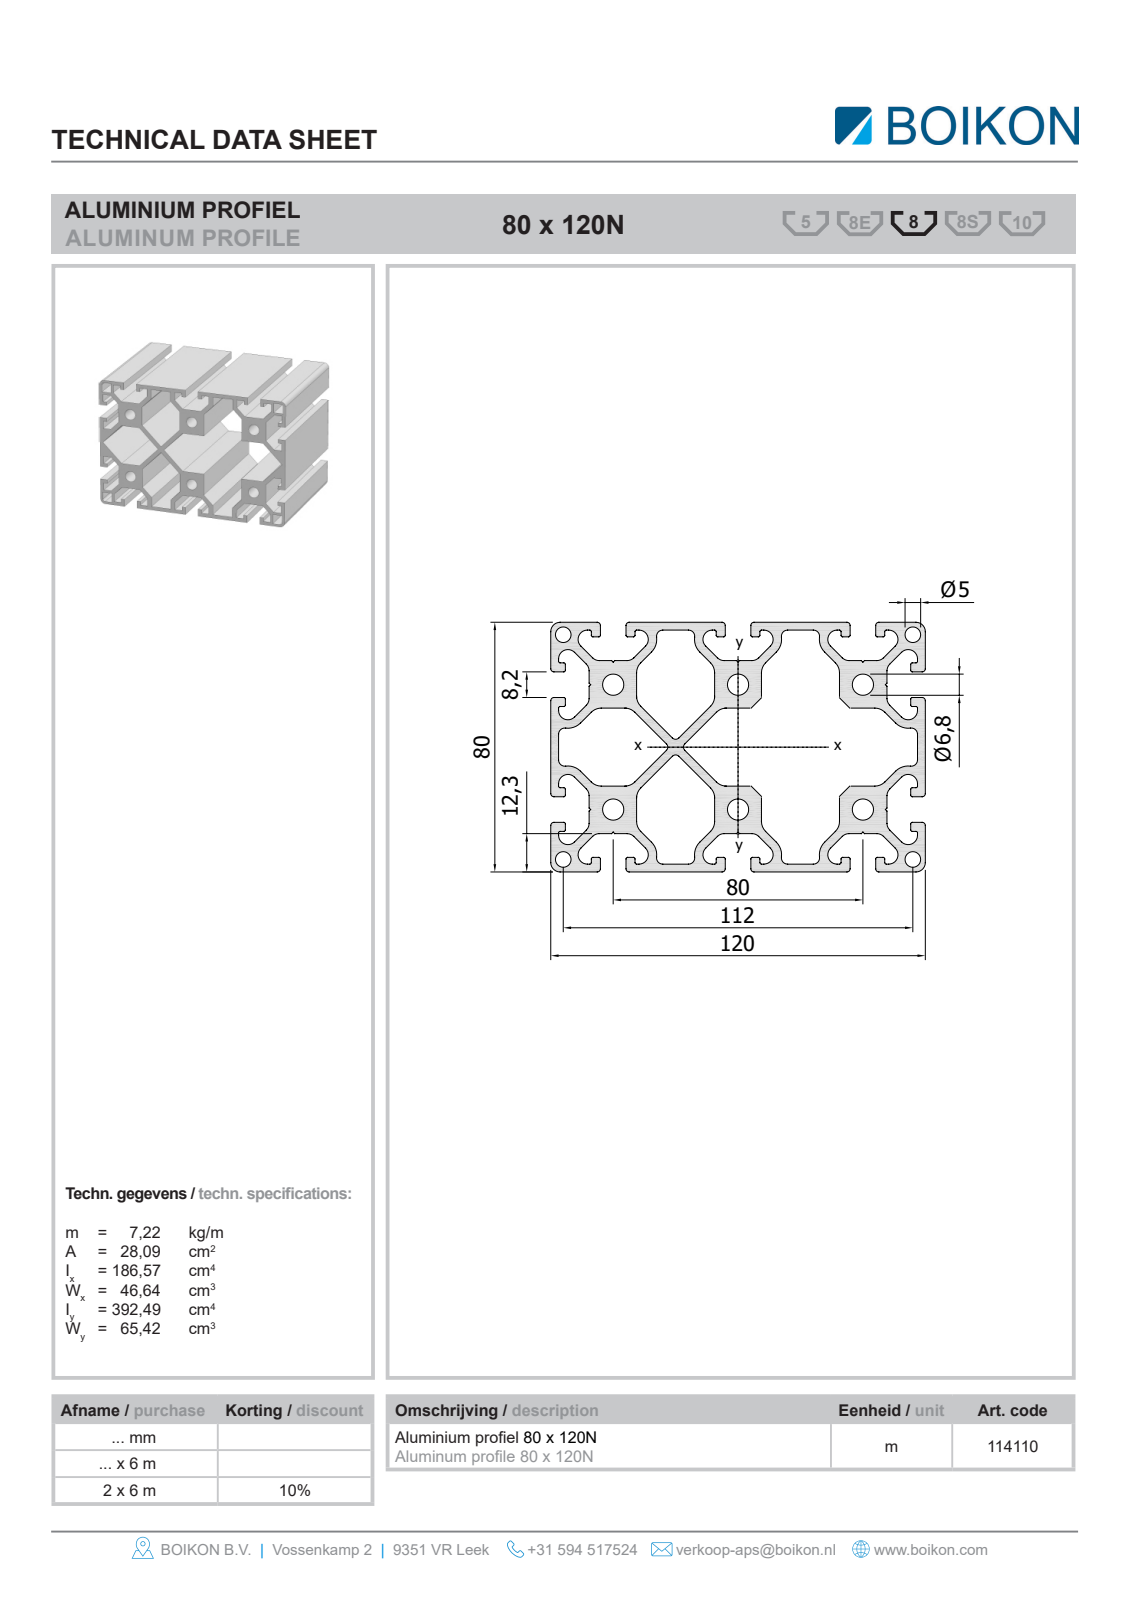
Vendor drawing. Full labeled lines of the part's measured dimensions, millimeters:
Part name (STEP PRODUCT): Root; 11411080x120NBOIKON0
STEP written by: HiCAD 2013 1802.4 Build 509 (AUTOMOTIVE_DESIGN)
Units: millimetres
Bodies: 1 solid, 222 faces (208 planar, 14 cylindrical, 0 other)
Overall size (bounding box): 1000 × 120 × 80
Volume: 2 782 000 mm³ · Surface area: 1 725 000 mm²
Round holes (diameter × count): ⌀6.8 ×6
Partial cylindrical surfaces — rounded edges, fillets, slot ends (radius × count): R1.5 ×4, R3 ×4
Main face-to-face distances: 40, 2.7, 28.28, 2.25, 80, 15.5, 56.56, 52.25, 27.75, 67.75
Hole centre spacings: 40, 56.57, 80, 89.44
